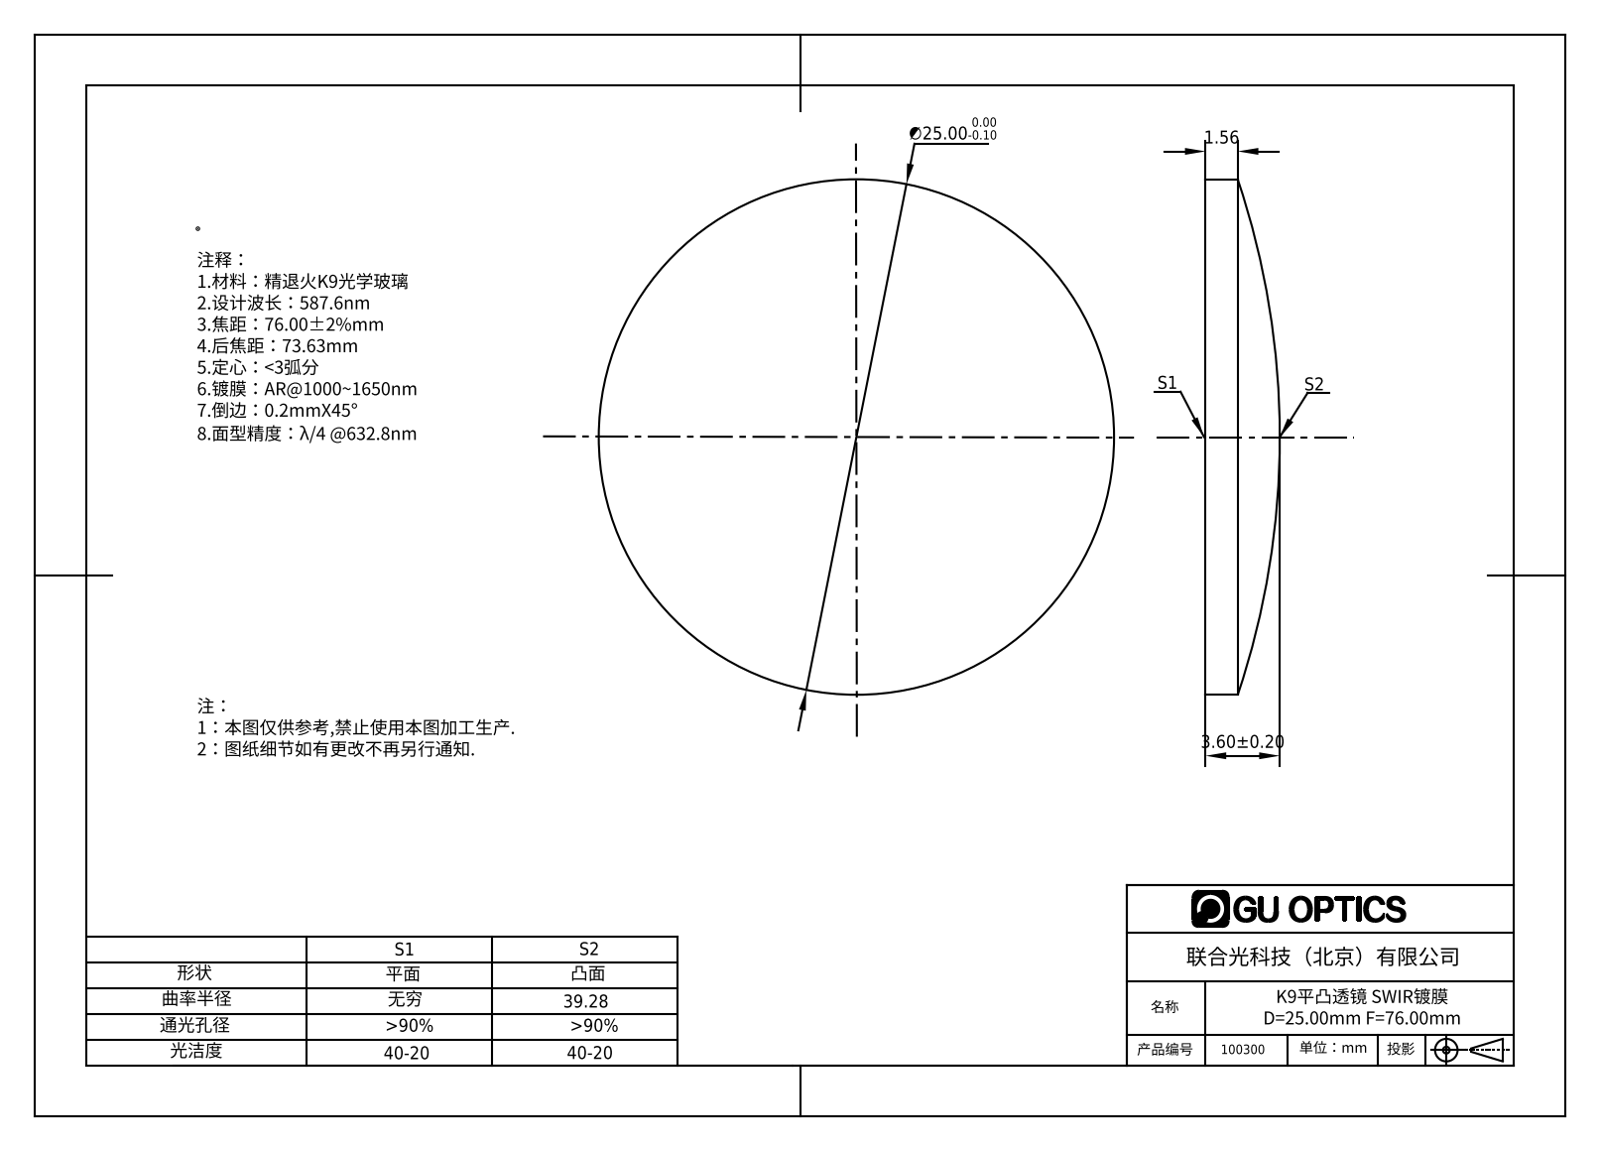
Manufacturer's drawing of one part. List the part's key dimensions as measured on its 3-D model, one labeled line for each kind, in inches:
Part name (STEP PRODUCT): 100128
STEP written by: SolidWorks 2016 (AUTOMOTIVE_DESIGN)
Units: inches
Bodies: 1 solid, 5 faces (1 planar, 2 cylindrical, 2 other)
Overall size (bounding box): 0.984 × 0.984 × 0.142
Volume: 0.078 in³ · Surface area: 1.731 in²
Round bosses / shafts (diameter × count): ⌀0.984 ×1
